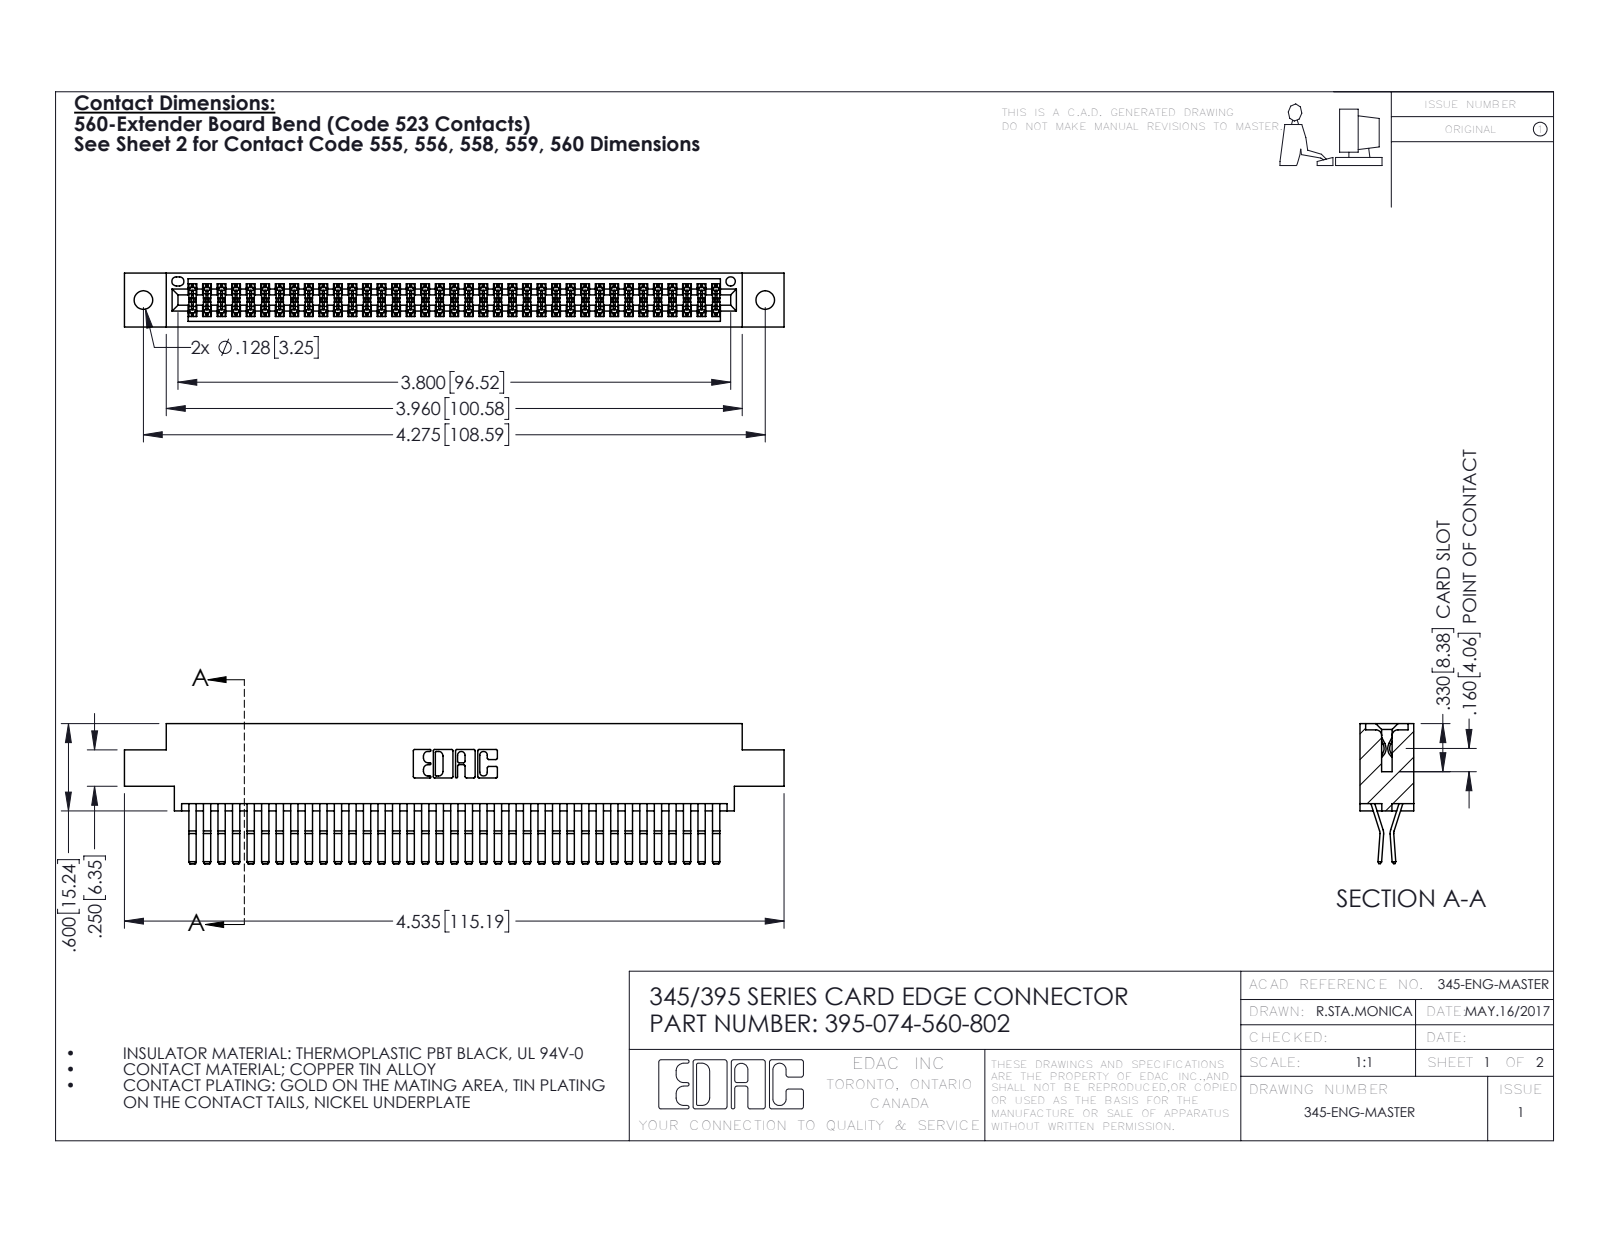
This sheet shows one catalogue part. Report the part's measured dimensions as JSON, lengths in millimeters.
{"part_name": "345-292-001_560 Tail; 395-074-560-802; 345 Part_0.170 Offset - 0.128 Dia", "step_written_by": "SolidWorks 2016 (CONFIG_CONTROL_DESIGN)", "units": "millimeters", "bodies": {"solids": 75, "faces": 3978, "planar": 2526, "cylindrical": 1452, "other": 0}, "overall_size": [115.2, 24.4, 9.4], "volume_mm3": 11500, "surface_area_mm2": 17990, "round_holes": [[3.3, 2], [1.6, 1]], "partial_cylinders_radius": [[0.2, 112], [0.3, 22], [0.2, 6], [0.8, 6], [0.7, 3], [0.3, 2], [0.4, 2], [0.5, 2]], "face_to_face_distances": [0.6, 7.6, 1.8, 9.4, 5.1, 2.5, 6.9, 5.7, 4.4, 3.8], "hole_center_spacings": [6.9, 102.6, 108.6]}
